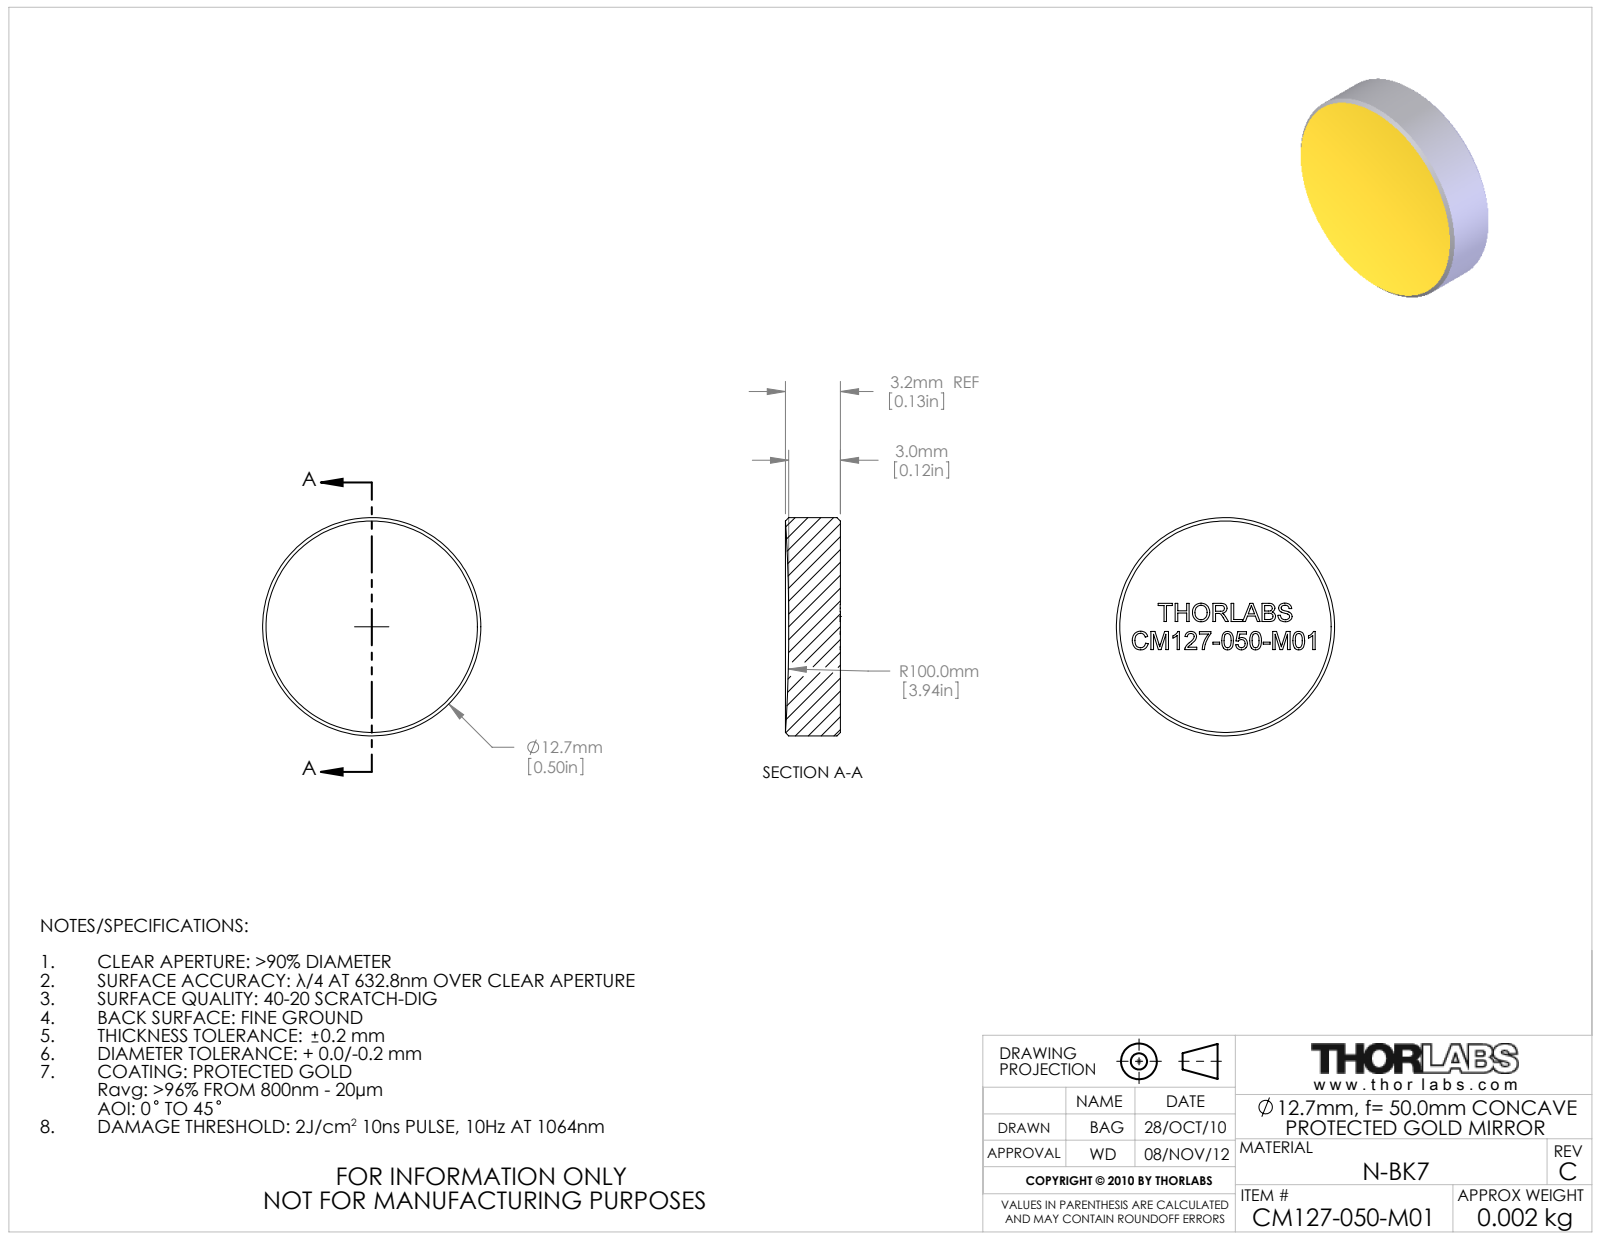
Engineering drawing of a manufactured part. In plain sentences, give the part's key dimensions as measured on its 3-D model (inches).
The part is named "17581-E0W". Its 3-D file was written by "SolidWorks 2009 (AUTOMOTIVE_DESIGN)". It is 1 solid with 268 faces: 151 planar, 2 cylindrical and 115 other. Overall it measures 0.5 by 0.5 by 0.126 inches. Its volume is 0.024 cubic inches and its surface area 0.576 square inches. Round bosses or shafts: 1 of diameter 0.5. The main face-to-face distances are 0.042, 0.064, 0.052, 0.048, 0.102, 0.03, 0.279, 0.036, 0.028, 0.034.
